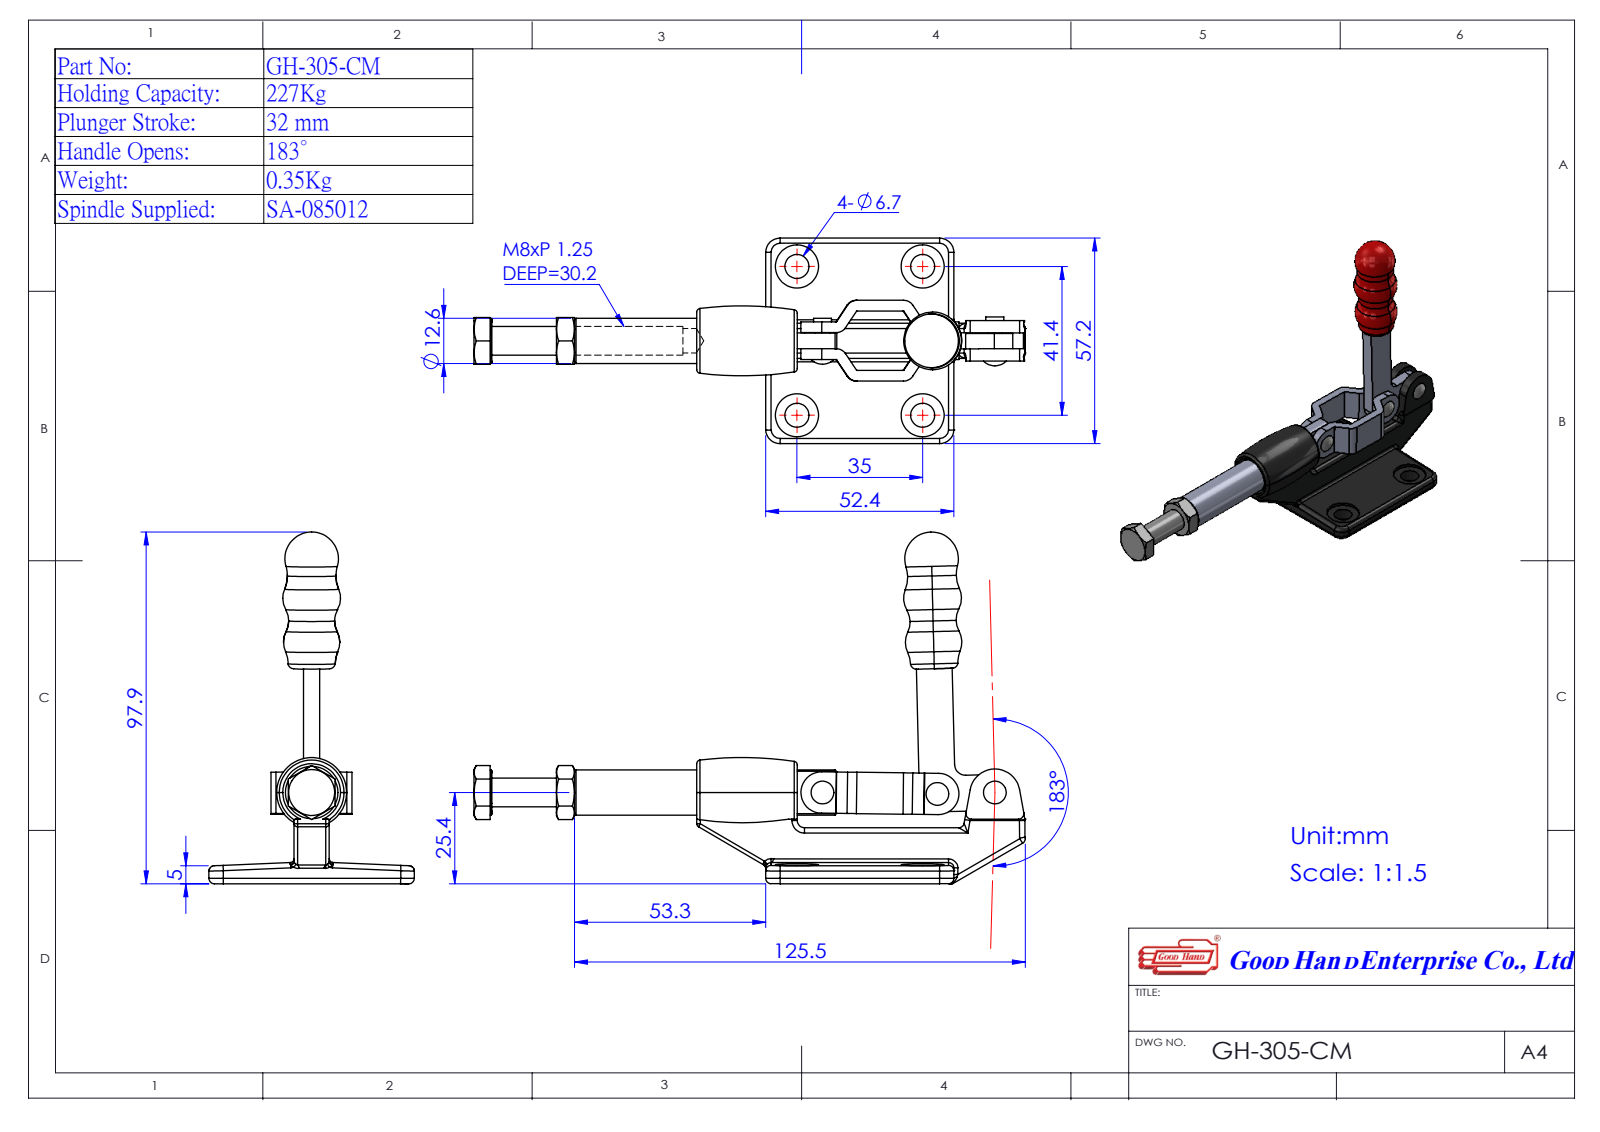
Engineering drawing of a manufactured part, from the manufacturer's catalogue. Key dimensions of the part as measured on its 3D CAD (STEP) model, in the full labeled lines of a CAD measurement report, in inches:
Part name (STEP PRODUCT): GH-305-CM(簡化)-1; 4304CM33-1^GH-305-CM(簡化)-1; Group5^GH-305-CM(簡化)-1; Group4^GH-305-CM(簡化)-1 (+2 more)
STEP written by: SolidWorks 2016 (AUTOMOTIVE_DESIGN)
Units: inches
Bodies: 5 solids, 262 faces (89 planar, 90 cylindrical, 83 other)
Overall size (bounding box): 6.046 × 3.854 × 2.252
Volume: 3.155 in³ · Surface area: 39.22 in²
Round holes (diameter × count): ⌀0.264 ×4, ⌀0.138 ×3, ⌀0.268 ×1, ⌀0.496 ×1
Round bosses / shafts (diameter × count): ⌀0.197 ×3, ⌀0.495 ×1, ⌀0.492 ×1, ⌀0.315 ×1
Partial cylindrical surfaces — rounded edges, fillets, slot ends (radius × count): R0.059 ×12, R0.039 ×8, R0.004 ×6, R0.157 ×5, R0.008 ×2, R0.016 ×2, R0.043 ×2, R0.226 ×2
Main face-to-face distances: 0.118, 0.106, 0.28, 0.386, 0.177, 0.102, 0.283, 0.531, 0.236, 0.65
Hole centre spacings: 1.378, 1.63, 2.134, 0.63, 1.259, 1.889
